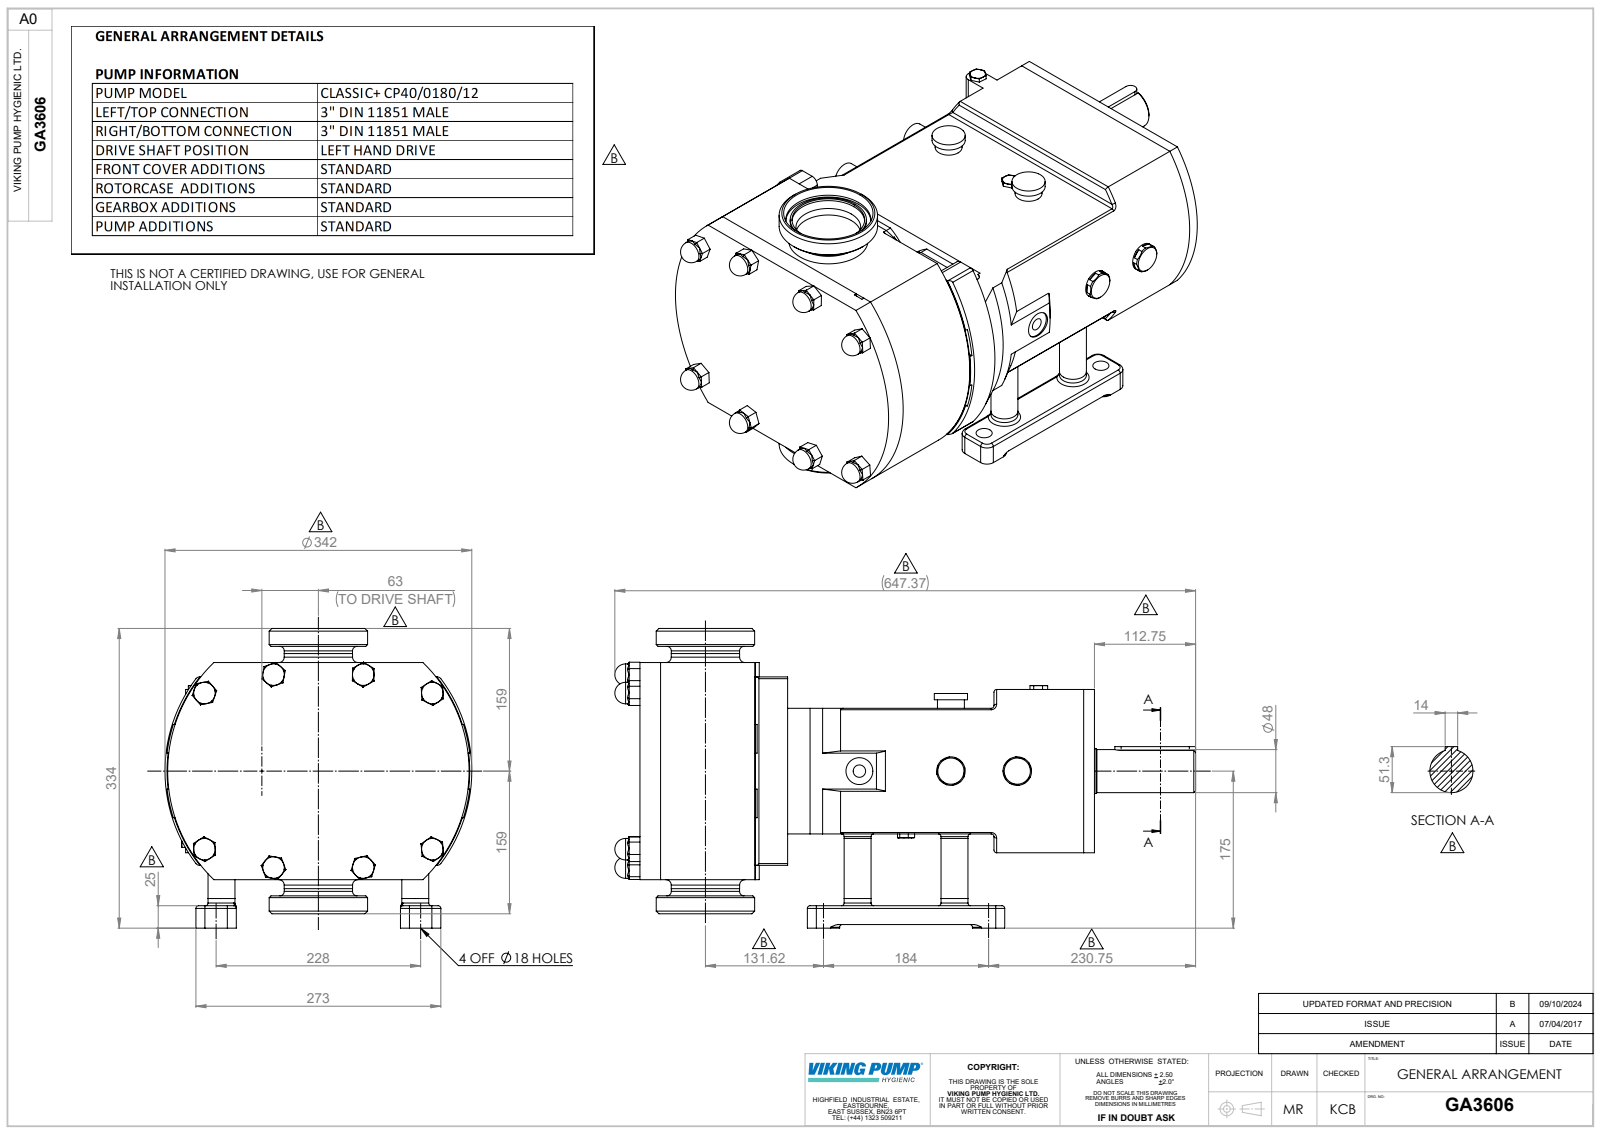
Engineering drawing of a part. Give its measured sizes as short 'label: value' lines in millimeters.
name: GA3606; Copy of Z94-5031-55 - 3 INCH DIN11851^GA3606; Copy (2) of CP40S-0180 V LHD^GA3606
written by: SolidWorks 2023 (AUTOMOTIVE_DESIGN)
unit: mm
bodies: 3 solids, 947 faces (363 planar, 279 cylindrical, 305 other)
size: 647.37 × 342 × 334
volume: 26 550 000 mm³; area: 940 111 mm²
holes: 4× ⌀10.2, 4× ⌀18, 2× ⌀11.89, 2× ⌀35, 1× ⌀13.83, 1× ⌀30, 1× ⌀72.2, 1× ⌀81, 1× ⌀94.8
bosses: 10× ⌀30, 8× ⌀24, 2× ⌀110, 2× ⌀70, 2× ⌀37, 2× ⌀31.75, 1× ⌀250, 1× ⌀109.7
rounds: 24× R10, 22× R3, 20× R8, 10× R6, 4× R5, 4× R11, 2× R7, 2× R15.24
face distances: 21, 161, 30, 51, 506.62, 191, 212, 140, 182, 242
hole spacings: 108, 54.04, 78.08, 96.05, 118.96, 126, 152.74, 174.13
